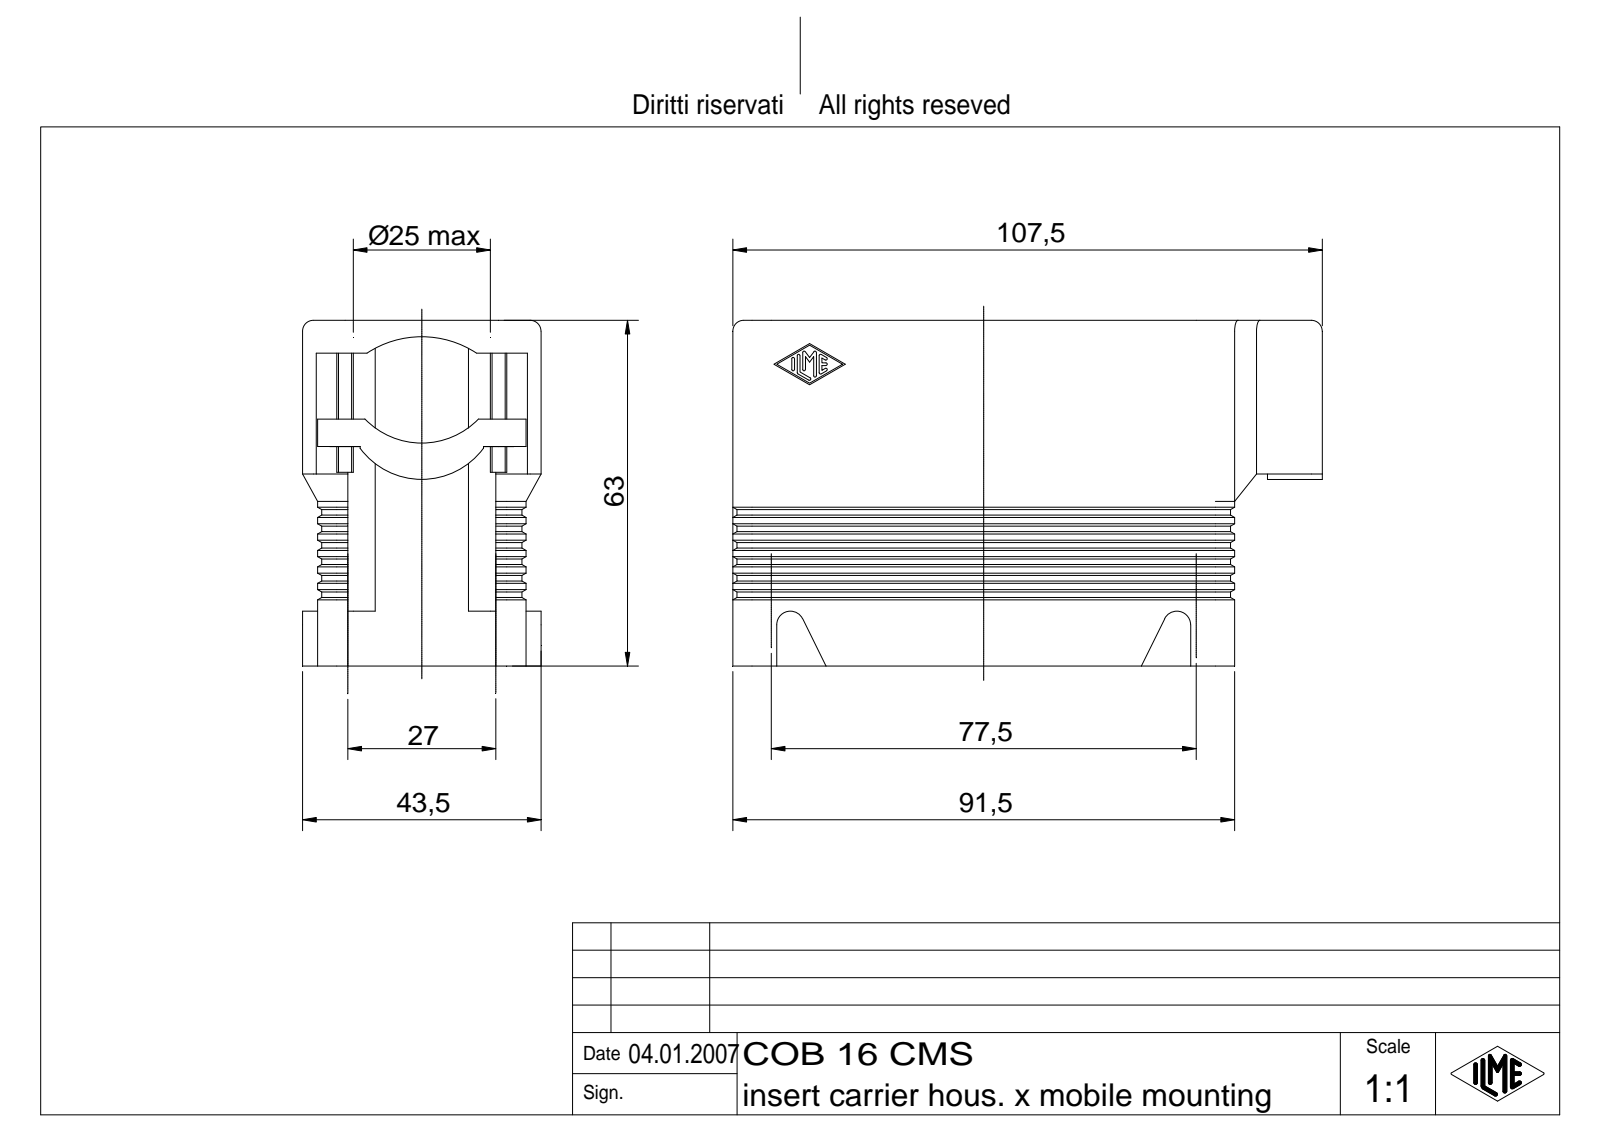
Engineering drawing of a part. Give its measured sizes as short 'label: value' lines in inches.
name: COB 16 CMS
written by: Autodesk Inventor 7 (AUTOMOTIVE_DESIGN)
unit: in
bodies: 6 solids, 559 faces (217 planar, 147 cylindrical, 195 other)
size: 4.232 × 2.48 × 1.713
volume: 3.083 in³; area: 73.53 in²
holes: 4× ⌀0.138
bosses: 4× ⌀0.137, 1× ⌀0.205, 1× ⌀0.118
rounds: 14× R0.01, 10× R0.079, 4× R0.059, 4× R0.138, 4× R0.157, 4× R0.197, 2× R0.02, 2× R0.098
face distances: 0.079, 1.417, 1.339, 1.496, 0.118, 1.388, 0.187, 0.138, 0.102, 0.108
hole spacings: 1.063, 3.051, 3.231
